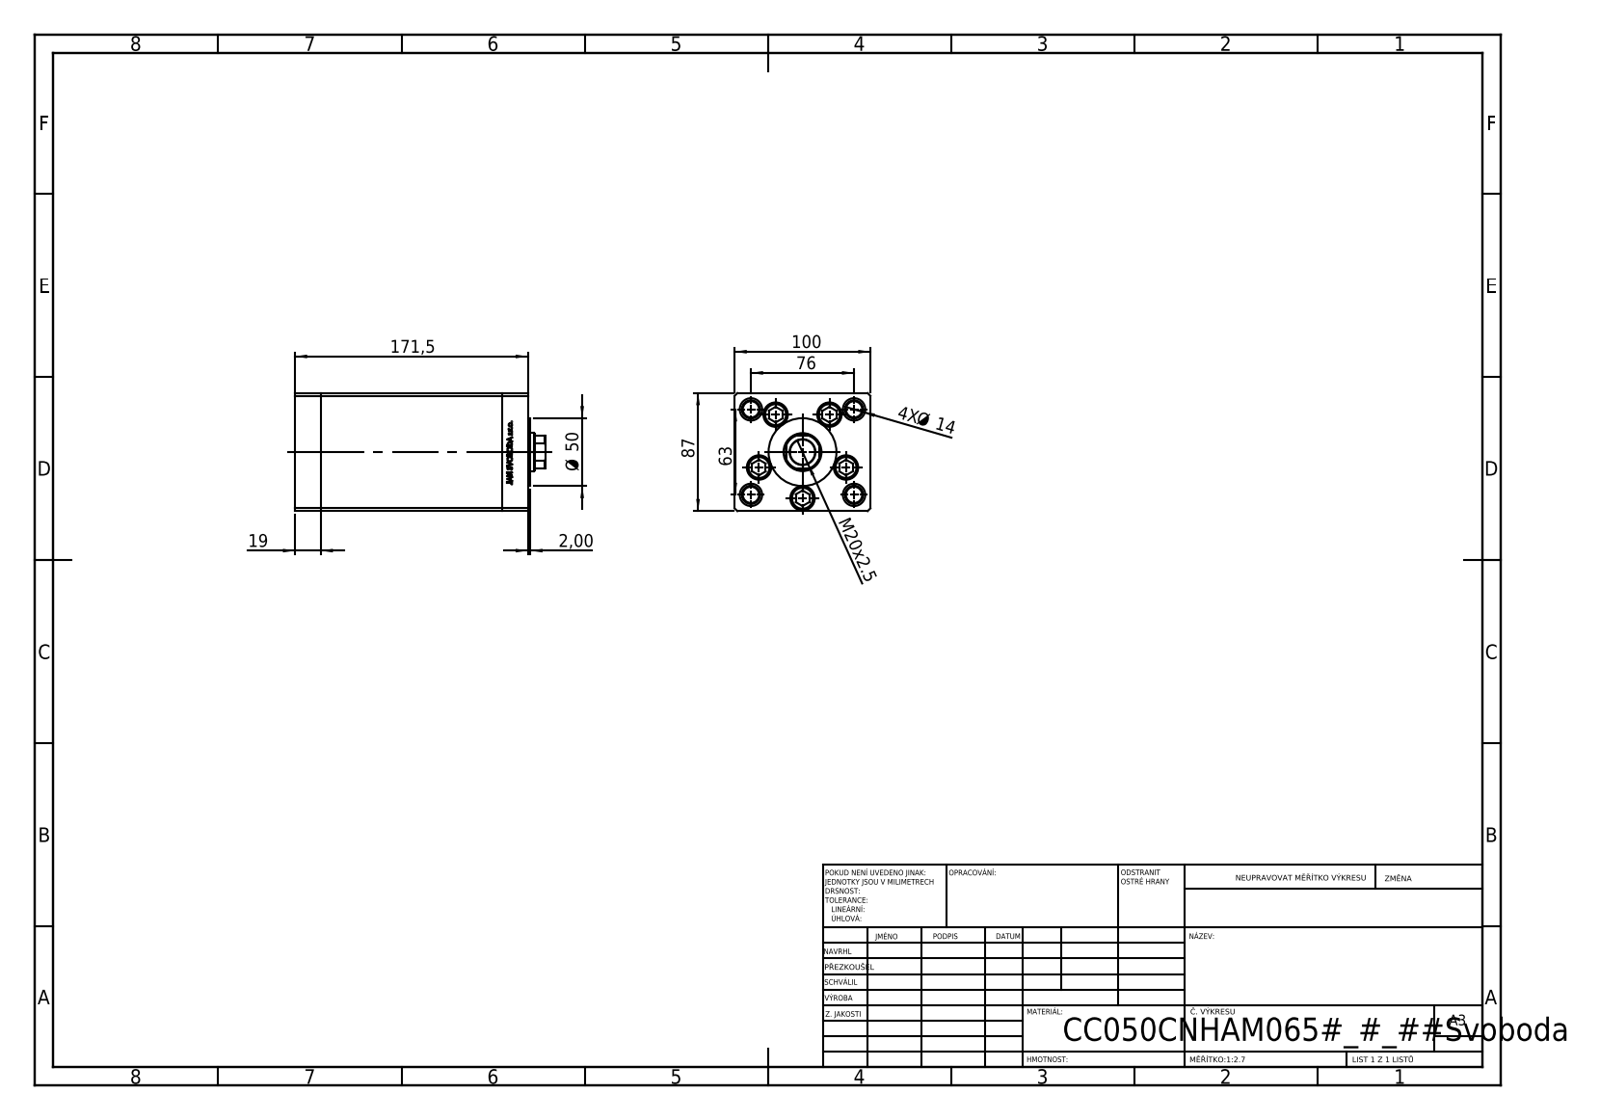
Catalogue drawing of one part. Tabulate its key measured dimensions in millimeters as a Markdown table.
| quantity | value |
| --- | --- |
| part name | ALLEN BOLT; V220C FRONT; V220C_VC_C; V220C_C MIDDLE (+1 more) |
| STEP written by | SolidWorks 2019 (CONFIG_CONTROL_DESIGN) |
| units | millimeters |
| bodies | 13 solids, 1182 faces (544 planar, 176 cylindrical, 462 other) |
| overall size | 184.5 × 100 × 87 |
| volume | 1 230 000 mm³ |
| surface area | 218 714 mm² |
| round holes (diameter × count) | 13.5 × 9, 18 × 5, 2 × 4, 12 × 4, 13.16 × 4, 16.5 × 4, 17 × 1, 18.5 × 1, 28 × 1 |
| round bosses / shafts (diameter × count) | 8 × 5, 17 × 4, 50 × 1 |
| partial cylindrical surfaces (radius × count) | 0.93 × 2, 13.5 × 1 |
| main face-to-face distances | 100, 87, 19, 133.5, 152.5, 34.25, 171.5, 137.25, 118.25, 15.25 |
| hole center spacings | 34, 49.36, 18.59, 21.03, 38.08, 39.27, 40.83, 43.24 |
